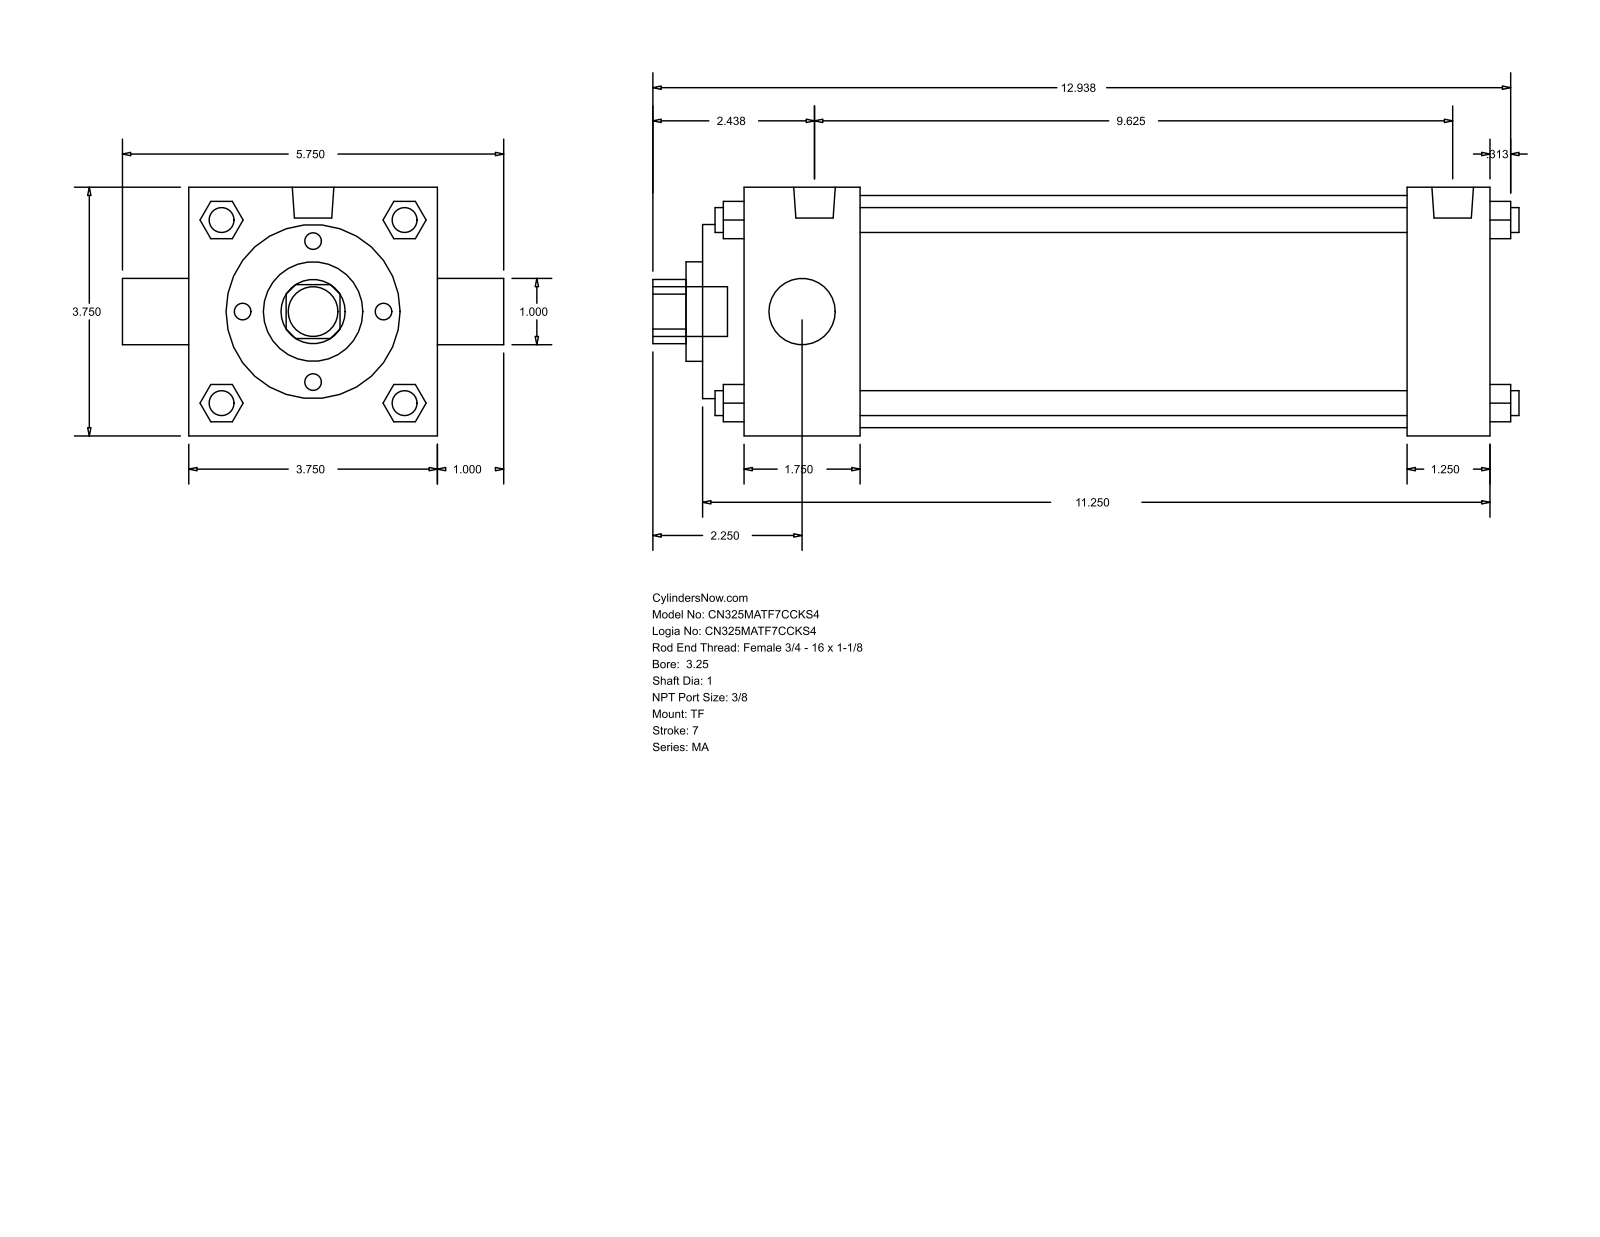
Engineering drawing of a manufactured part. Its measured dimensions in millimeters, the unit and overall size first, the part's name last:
Units: millimetres
Overall size (bounding box): 331.79 × 146.05 × 95.25
Round holes (diameter × count): ⌀25.4 ×2, ⌀38.1 ×1, ⌀66.67 ×1, ⌀88.9 ×1
Round bosses / shafts (diameter × count): ⌀9.53 ×4, ⌀11.11 ×3, ⌀15.93 ×2, ⌀19.05 ×1
Partial cylindrical surfaces — rounded edges, fillets, slot ends (radius × count): R12.29 ×1
Main face-to-face distances: 95.24, 285.76, 15.87, 44.46, 254.01, 209.55, 241.3, 31.75, 60.33, 269.88
Bodies: 0 solids, 122 faces (93 planar, 29 cylindrical, 0 other)
Part name (STEP PRODUCT): MA_TF__0325_1
STEP written by: GSSL Pune (CONFIG_CONTROL_DESIGN)
